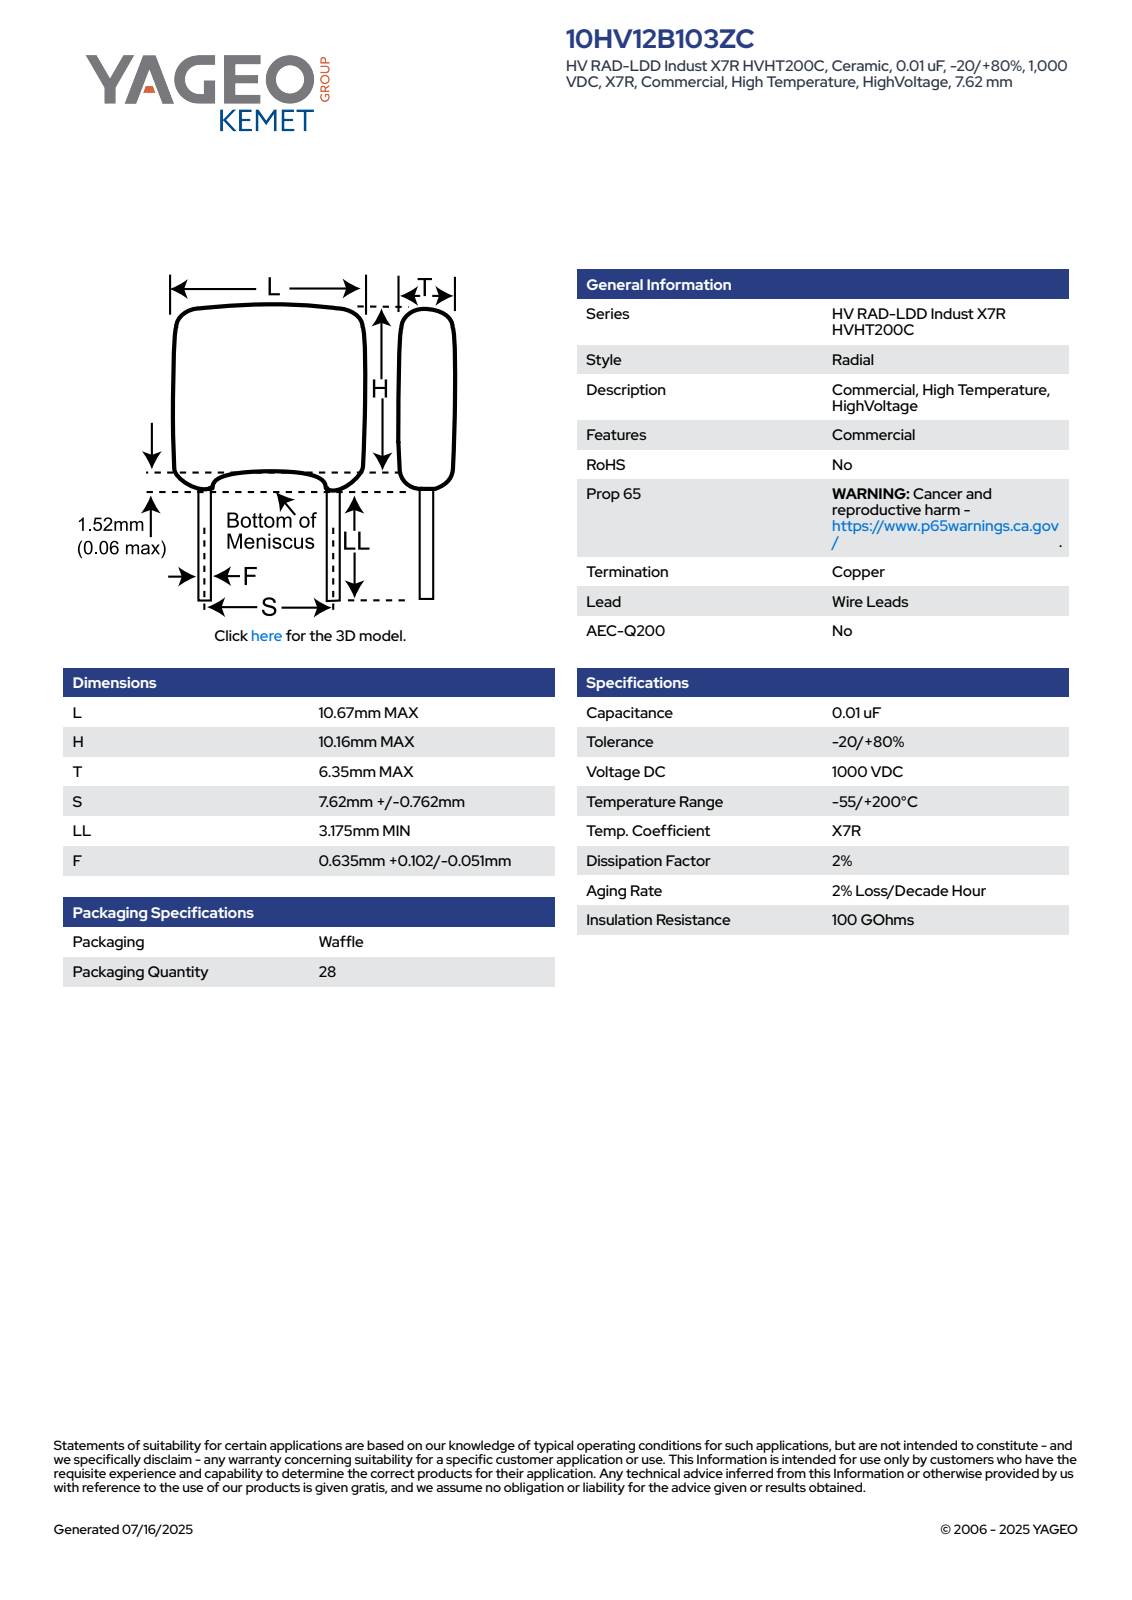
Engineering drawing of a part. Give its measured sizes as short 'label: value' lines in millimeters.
name: CCR_RCST_HV12_L10.67H10.16T6.35S7.62LL31.75F0.735
written by: SolidWorks 2014 (AUTOMOTIVE_DESIGN)
unit: mm
bodies: 4 solids, 94 faces (66 planar, 18 cylindrical, 10 other)
size: 43.49 × 10.67 × 6.36
volume: 752 mm³; area: 643 mm²
bosses: 2× ⌀0.74
rounds: 8× R1, 4× R0.5
face distances: 6.35, 10.67, 11.74, 31.75, 43.49, 5.18, 38.31, 6.56, 36.95, 5.2
